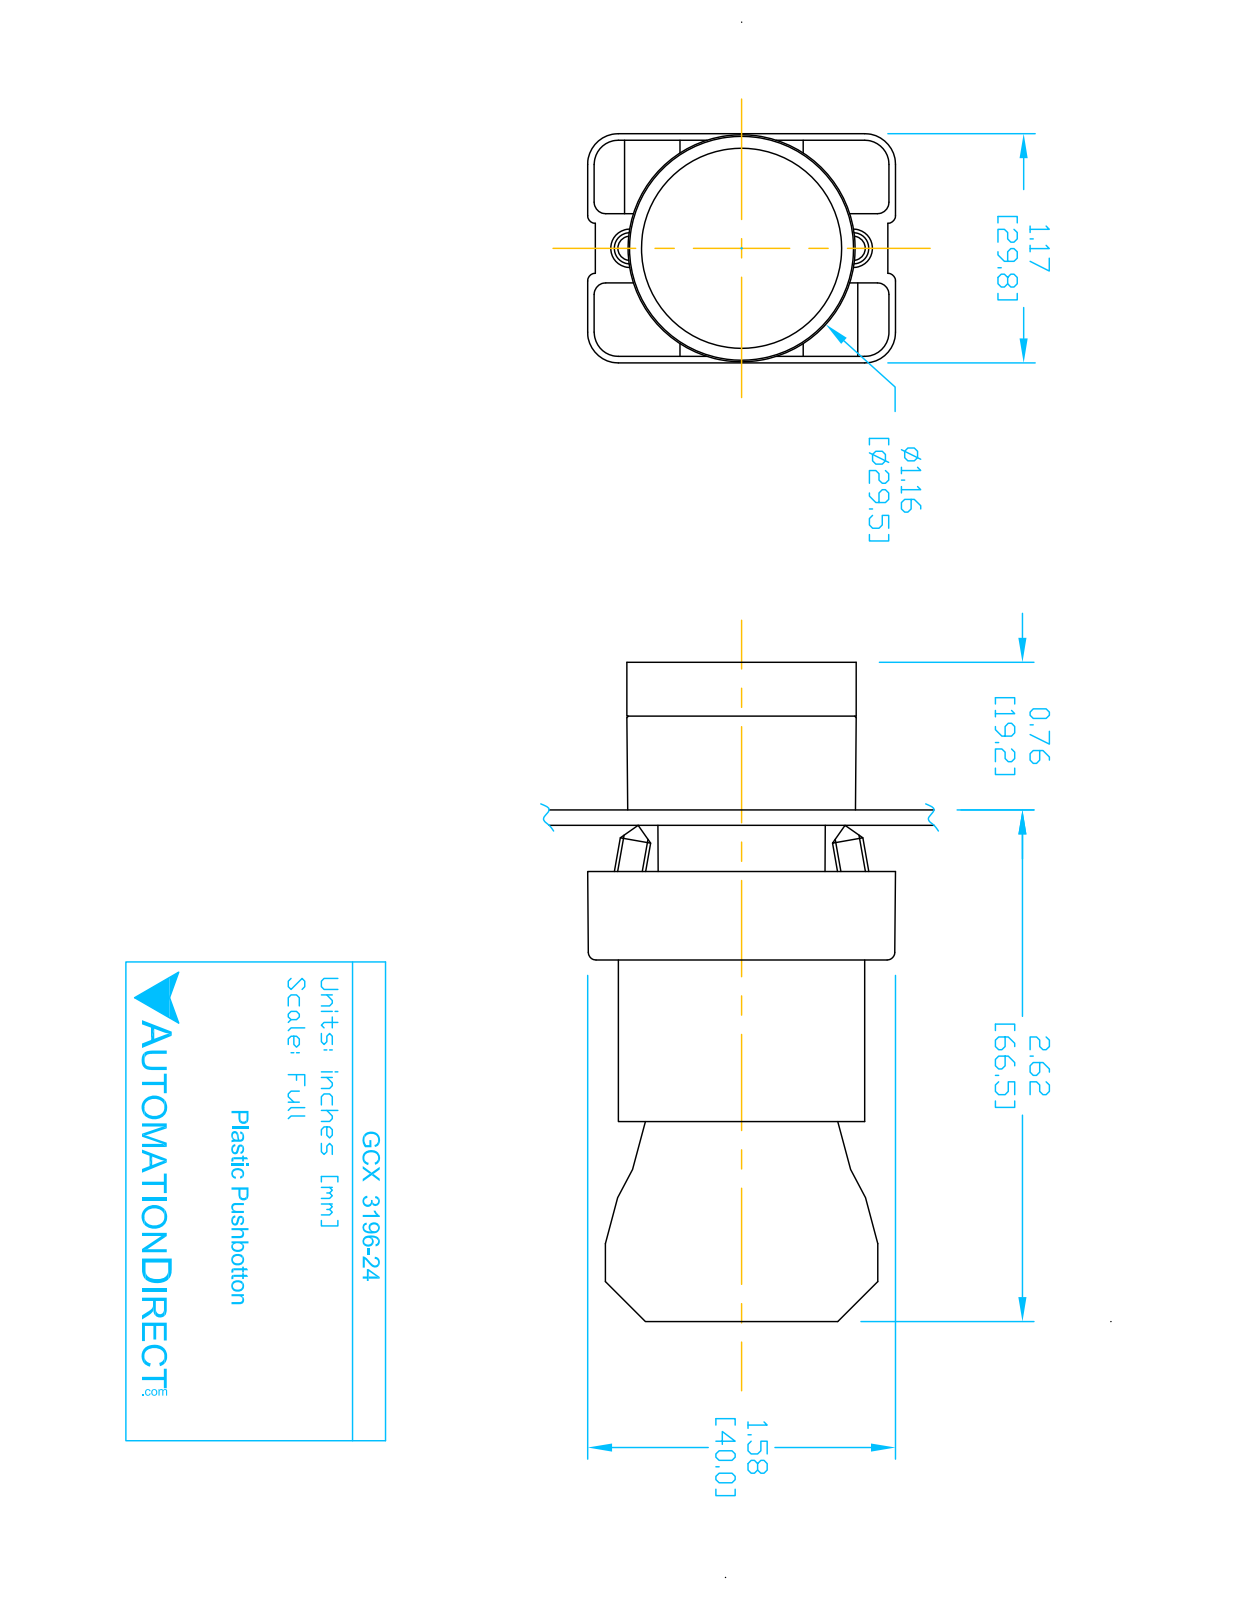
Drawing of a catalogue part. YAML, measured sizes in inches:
part_name: "ECX1050; GCX3196-24; GCX3196 OPERATOR; CONTACT BLOCK (+1 more)"
step_written_by: "SolidWorks 2016 (AUTOMOTIVE_DESIGN)"
units: inches
bodies: {solids: 8, faces: 431, planar: 252, cylindrical: 148, other: 31}
overall_size: [3.319, 1.581, 1.177]
volume: 2.794
surface_area: 38.77
round_holes:
  - {diameter: 0.079, count: 2}
  - {diameter: 0.124, count: 2}
  - {diameter: 0.13, count: 2}
  - {diameter: 0.087, count: 1}
  - {diameter: 0.197, count: 1}
  - {diameter: 0.469, count: 1}
  - {diameter: 0.878, count: 1}
  - {diameter: 0.888, count: 1}
  - {diameter: 1.024, count: 1}
round_bosses_or_shafts:
  - {diameter: 0.157, count: 4}
  - {diameter: 1.175, count: 1}
  - {diameter: 1.004, count: 1}
  - {diameter: 0.945, count: 1}
  - {diameter: 0.856, count: 1}
  - {diameter: 0.78, count: 1}
  - {diameter: 0.504, count: 1}
partial_cylinders:
  - {radius: 0.059, count: 24}
  - {radius: 0.041, count: 12}
  - {radius: 0.124, count: 12}
  - {radius: 0.157, count: 12}
  - {radius: 0.039, count: 8}
  - {radius: 0.128, count: 2}
  - {radius: 0.02, count: 1}
  - {radius: 0.063, count: 1}
face_to_face_distances: [0.827, 0.579, 2.02, 1.193, 1.171, 0.276, 2.295, 1.469, 0.031, 0.033]
hole_center_spacings: [0.236, 0.544, 0.472, 0.49]
